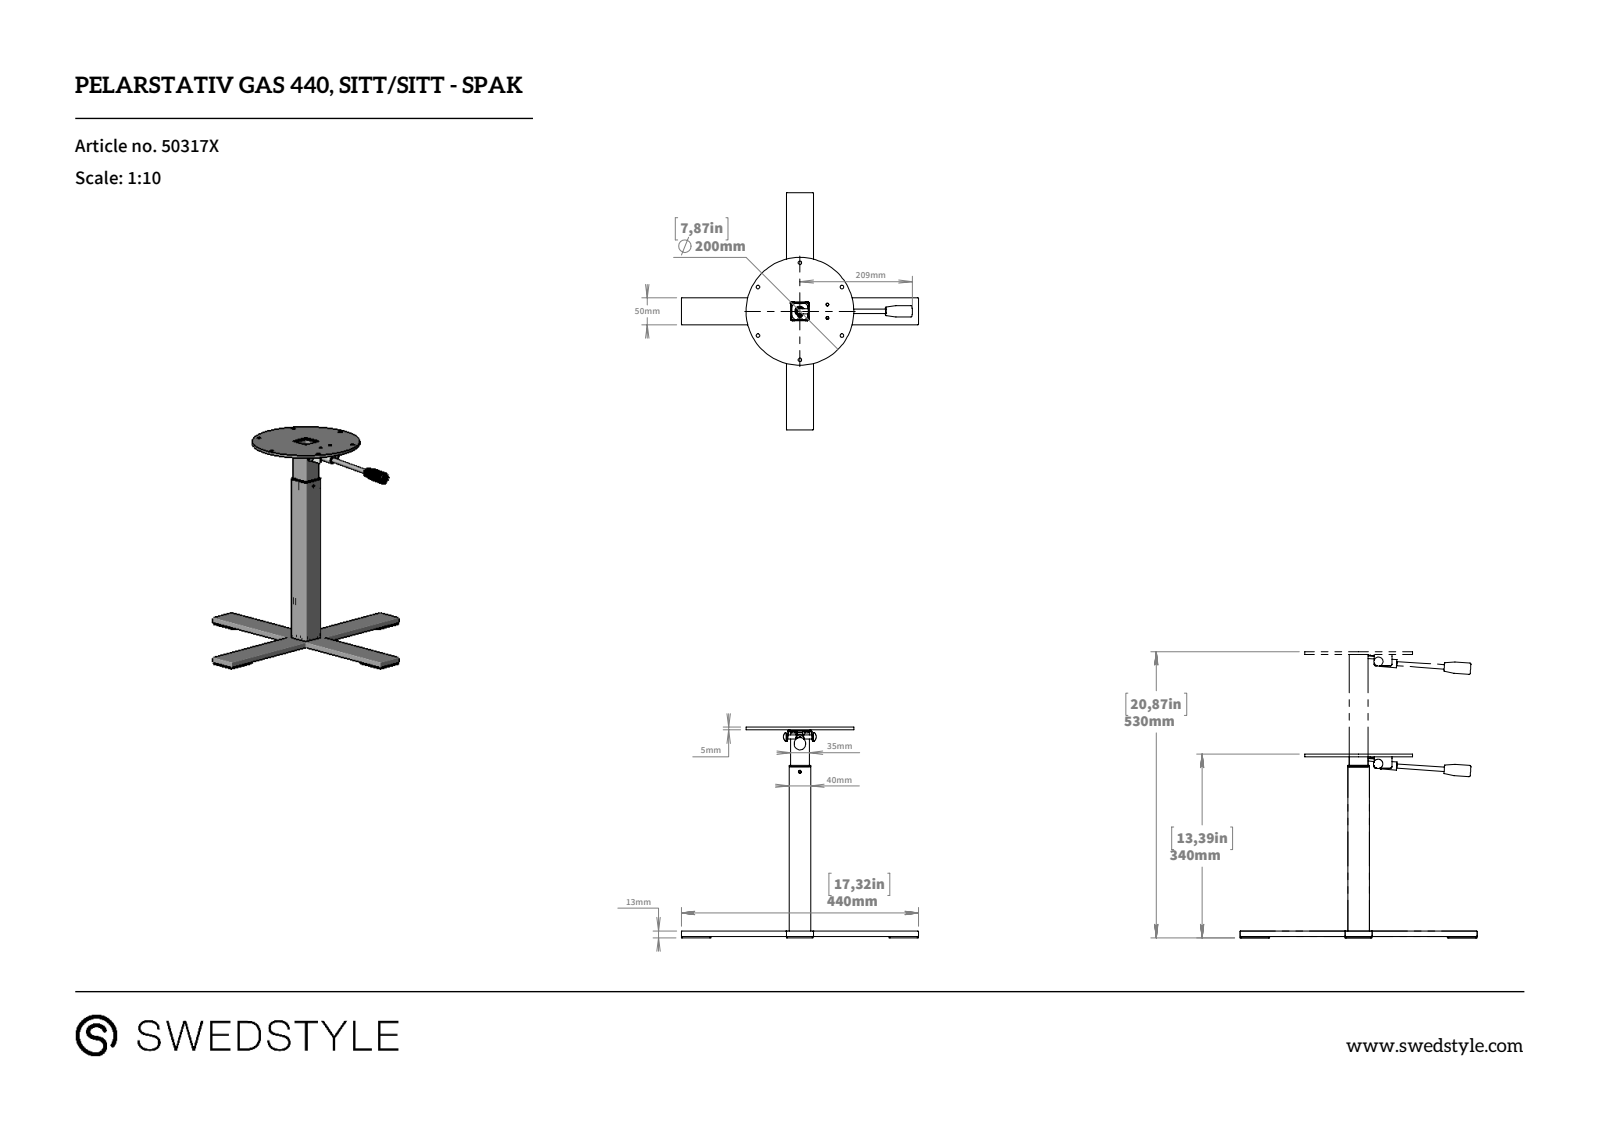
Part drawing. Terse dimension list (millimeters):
name: 50317x_Pelarstativ gas 440, spak, Sitt_Sitt
written by: SolidWorks 2017 (CONFIG_CONTROL_DESIGN)
unit: mm
bodies: 0 solids, 285 faces (112 planar, 115 cylindrical, 58 other)
size: 440 × 440 × 390.6
holes: 10× ⌀6.6, 2× ⌀5, 1× ⌀5.2
bosses: 2× ⌀8, 1× ⌀200, 1× ⌀21, 1× ⌀15
rounds: 24× R1, 18× R2, 16× R3, 4× R0.4, 4× R2.5, 2× R4, 1× R6
face distances: 2.5, 5, 10, 2, 37.5, 4.5, 35.5, 33, 388.1, 378.1
hole spacings: 90, 155.88, 26, 72.4, 78.09, 87.07, 96.41, 103.82
